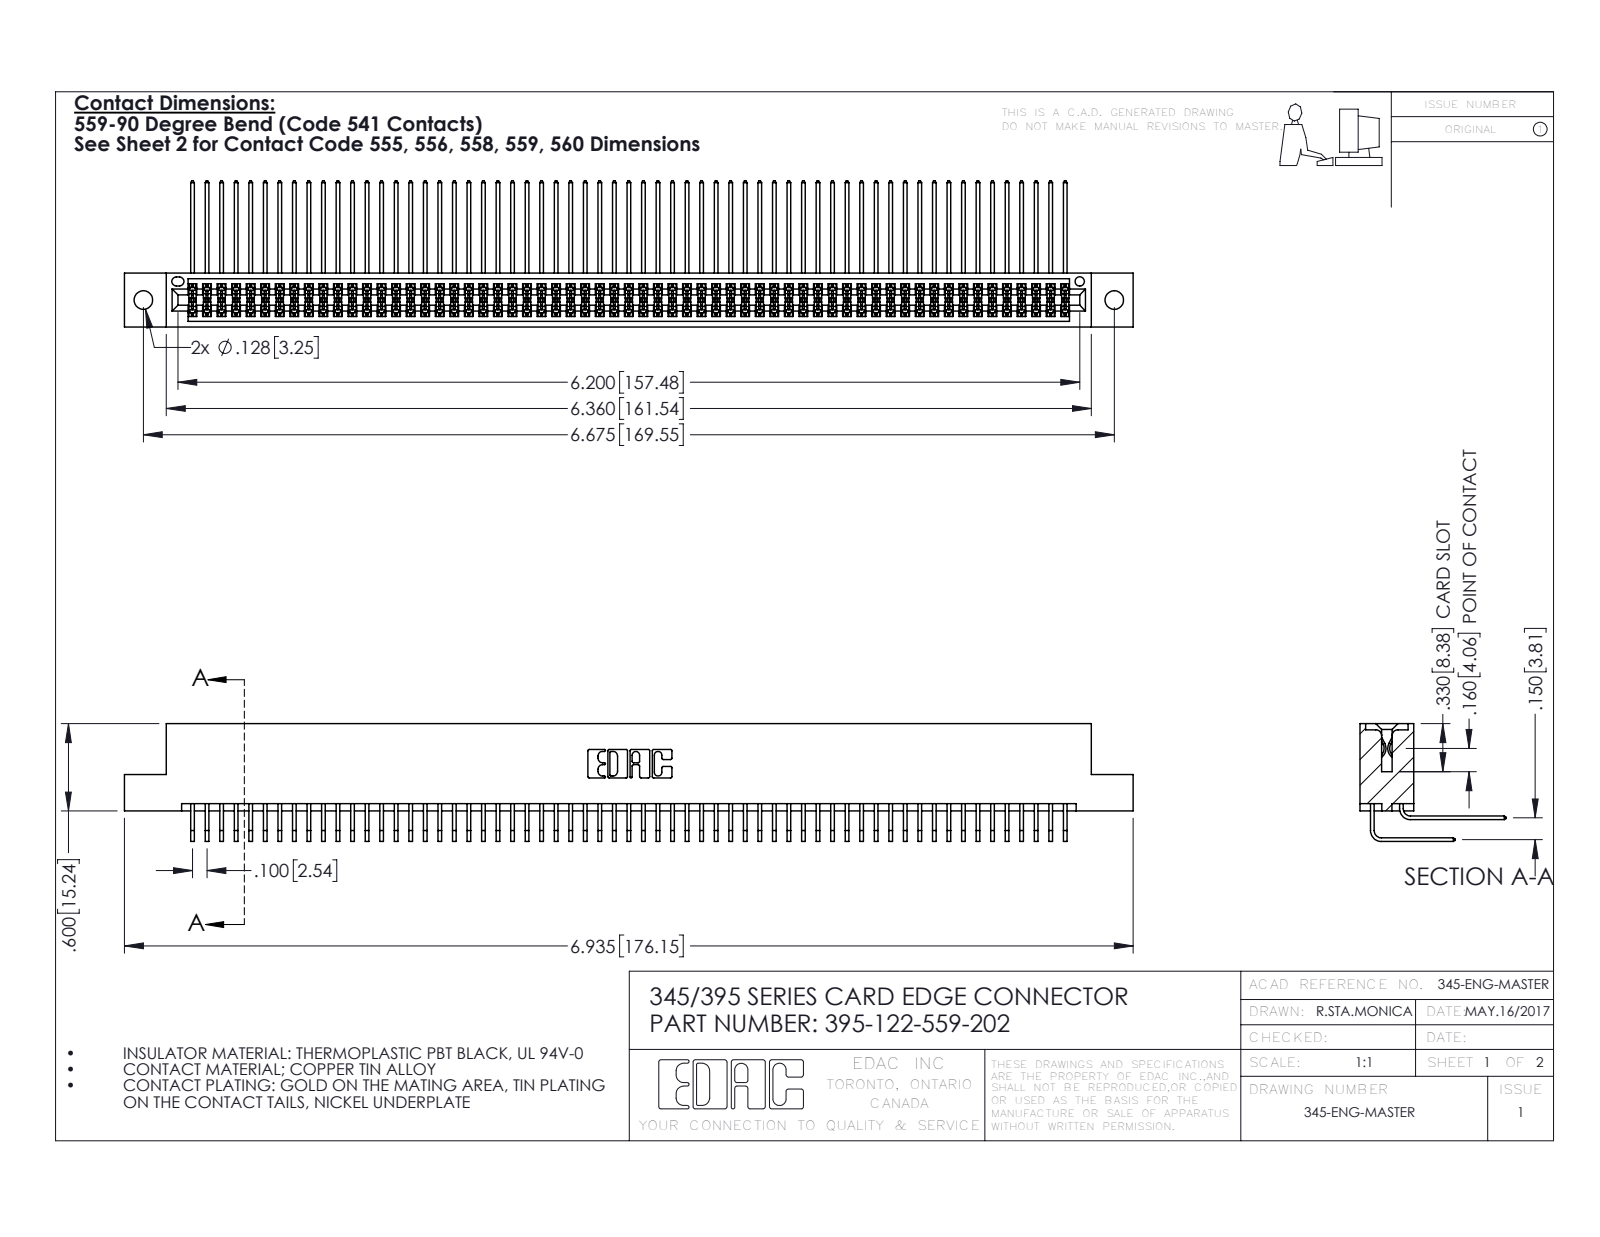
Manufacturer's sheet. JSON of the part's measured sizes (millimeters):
{"part_name": "345-292-001_558 559 Tail - 1; 345 Part_Flush Mounting Lugs - 0.128 Dia; 345-292-001_559 Tail - 2; 395-122-559-202", "step_written_by": "SolidWorks 2016 (CONFIG_CONTROL_DESIGN)", "units": "millimeters", "bodies": {"solids": 123, "faces": 6470, "planar": 4350, "cylindrical": 2120, "other": 0}, "overall_size": [176.1, 25.5, 20.5], "volume_mm3": 17960, "surface_area_mm2": 29940, "round_holes": [[3.3, 2], [1.6, 1]], "partial_cylinders_radius": [[0.2, 183], [0.3, 22], [0.2, 6], [0.8, 6], [0.7, 3], [0.4, 2], [0.5, 2], [0.6, 2]], "face_to_face_distances": [1.8, 7.6, 5.1, 9.4, 2.5, 6.9, 0.6, 5.7, 4.4, 3.8], "hole_center_spacings": [6.9, 163.6, 169.5]}
